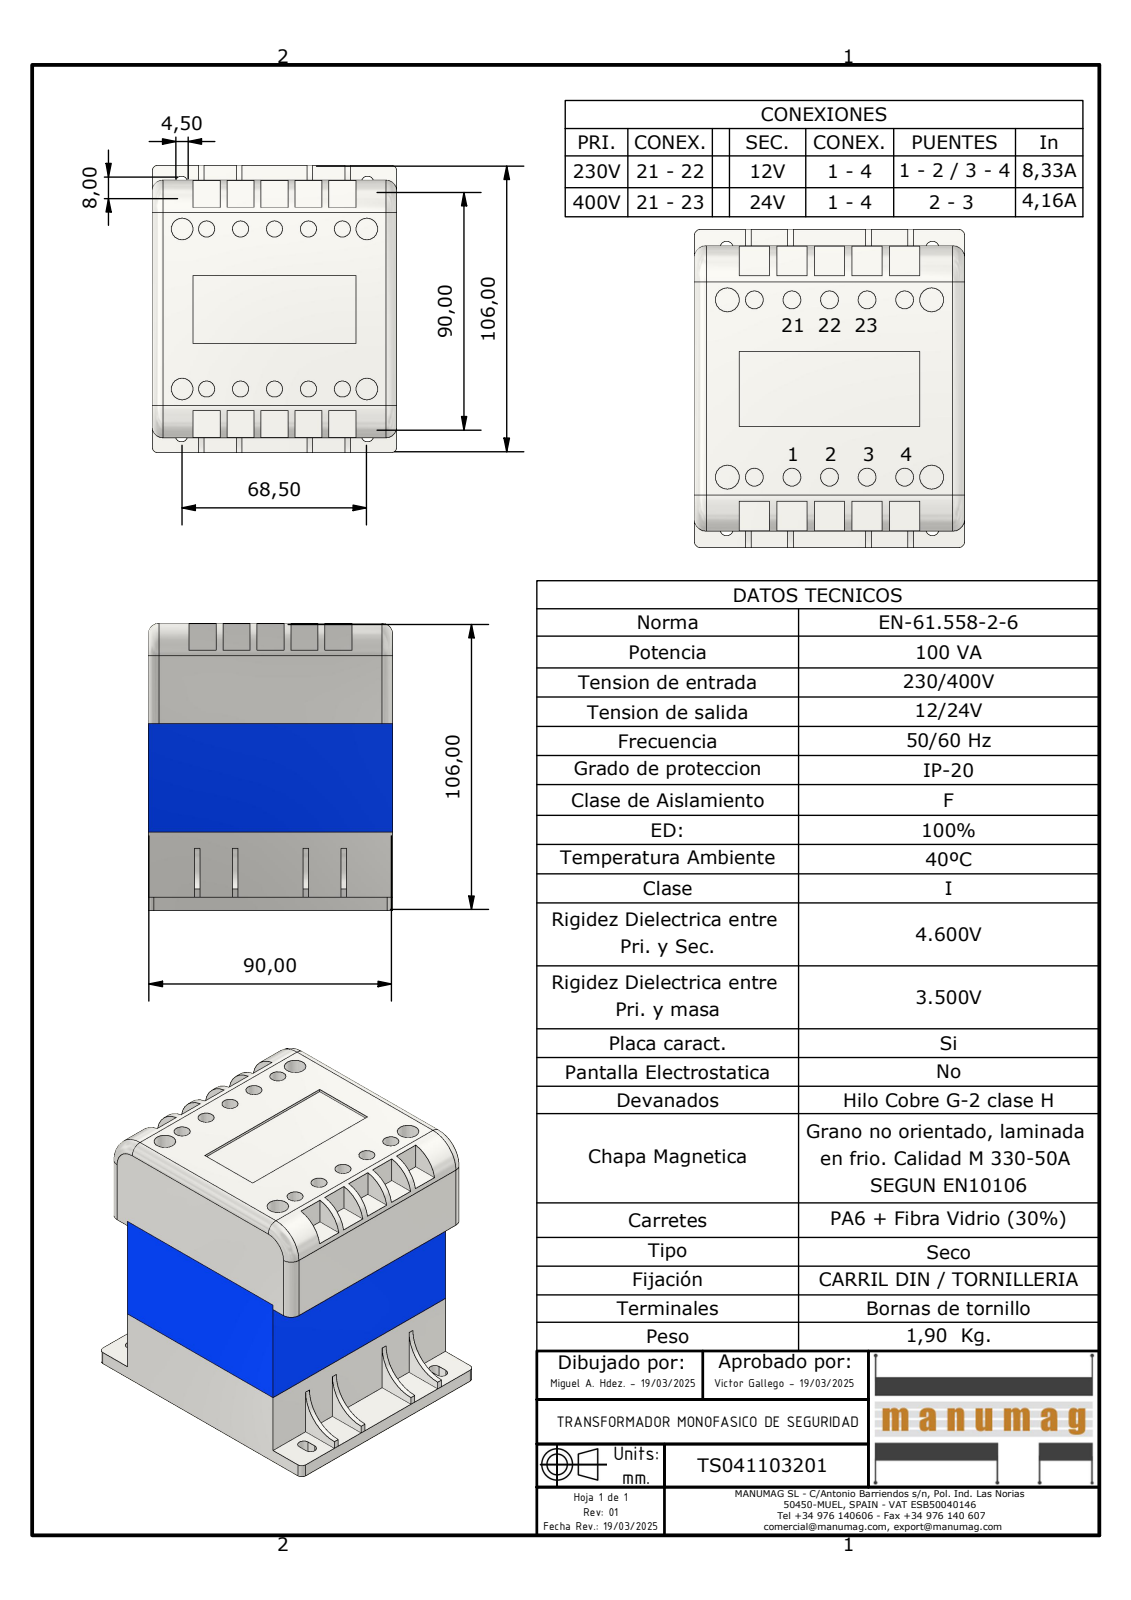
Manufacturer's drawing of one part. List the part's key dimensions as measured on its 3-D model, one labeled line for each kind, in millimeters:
Part name (STEP PRODUCT): TS041103201; CENTRAL EI84-40; SUPERIOR EI84; INFERIOR EI84
STEP written by: Autodesk Inventor 2023 (AUTOMOTIVE_DESIGN)
Units: millimetres
Bodies: 11 solids, 188 faces (142 planar, 42 cylindrical, 4 other)
Overall size (bounding box): 106 × 106 × 90
Volume: 352 957 mm³ · Surface area: 101 743 mm²
Round holes (diameter × count): ⌀6 ×10, ⌀8 ×4
Partial cylindrical surfaces — rounded edges, fillets, slot ends (radius × count): R2.25 ×8, R4 ×6, R2 ×4, R12 ×2, R15 ×2
Main face-to-face distances: 1, 75, 89, 5, 90, 71, 66, 76, 74, 88
Hole centre spacings: 59, 12.5, 60.31, 25, 64.08, 9, 21.5, 34
